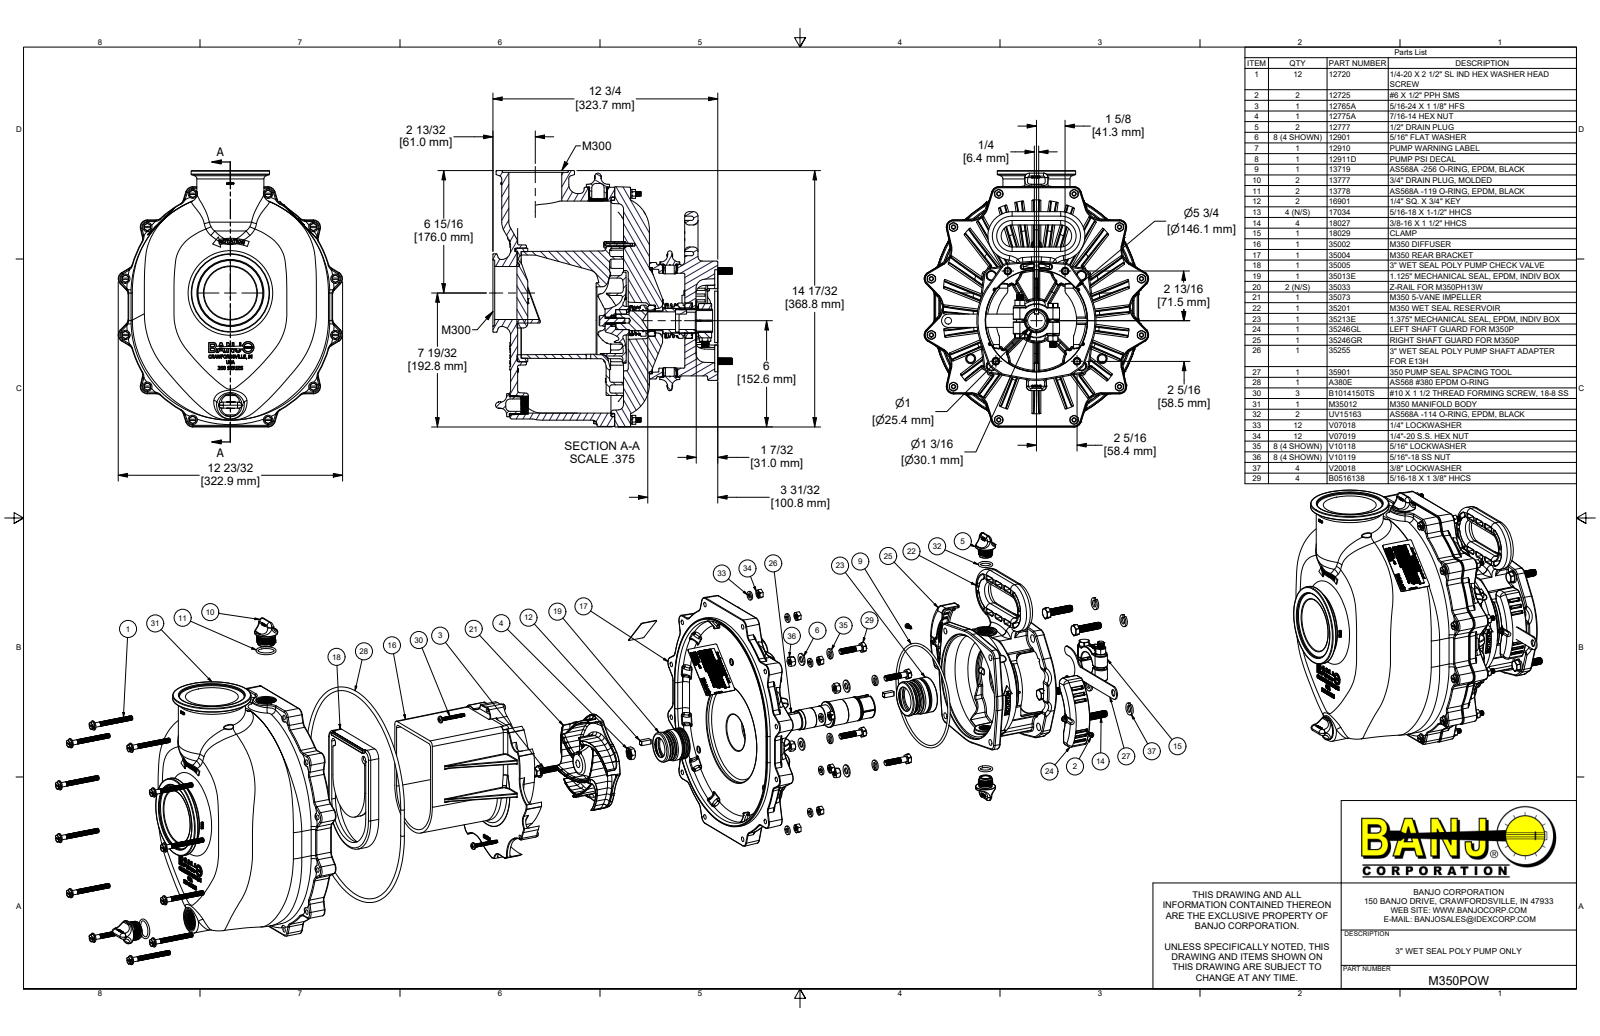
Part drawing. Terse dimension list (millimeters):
name: M350POW; 35073; 35002; M35012 (+8 more)
written by: Autodesk Inventor 2022 (AUTOMOTIVE_DESIGN)
unit: mm
bodies: 107 solids, 24156 faces (8479 planar, 3707 cylindrical, 11970 other)
size: 368.8 × 344.8 × 322.9
volume: 5 622 000 mm³; area: 1 545 000 mm²
holes: 12× ⌀5, 12× ⌀6.4, 12× ⌀6.9, 10× ⌀13.2, 6× ⌀9.8, 5× ⌀11.1, 4× ⌀6.4, 4× ⌀8, 4× ⌀8.2, 4× ⌀8.7, 4× ⌀8.7, 3× ⌀3.2
bosses: 92× ⌀8.2, 46× ⌀8.6, 12× ⌀12.4, 12× ⌀6.4, 6× ⌀17.4, 6× ⌀9.5, 4× ⌀17.5, 4× ⌀14.8
rounds: 309× R0.8, 195× R1.6, 75× R0.4, 69× R2.4, 53× R6.4, 52× R3.2, 49× R9.5, 26× R3
face distances: 10.2, 162.6, 12.7, 22.9, 127.4, 102.9, 5.1, 139.7, 6.8, 169.4
hole spacings: 152.5, 80.8, 238.9, 91.7, 129.7, 155.9, 158.4, 162.8
